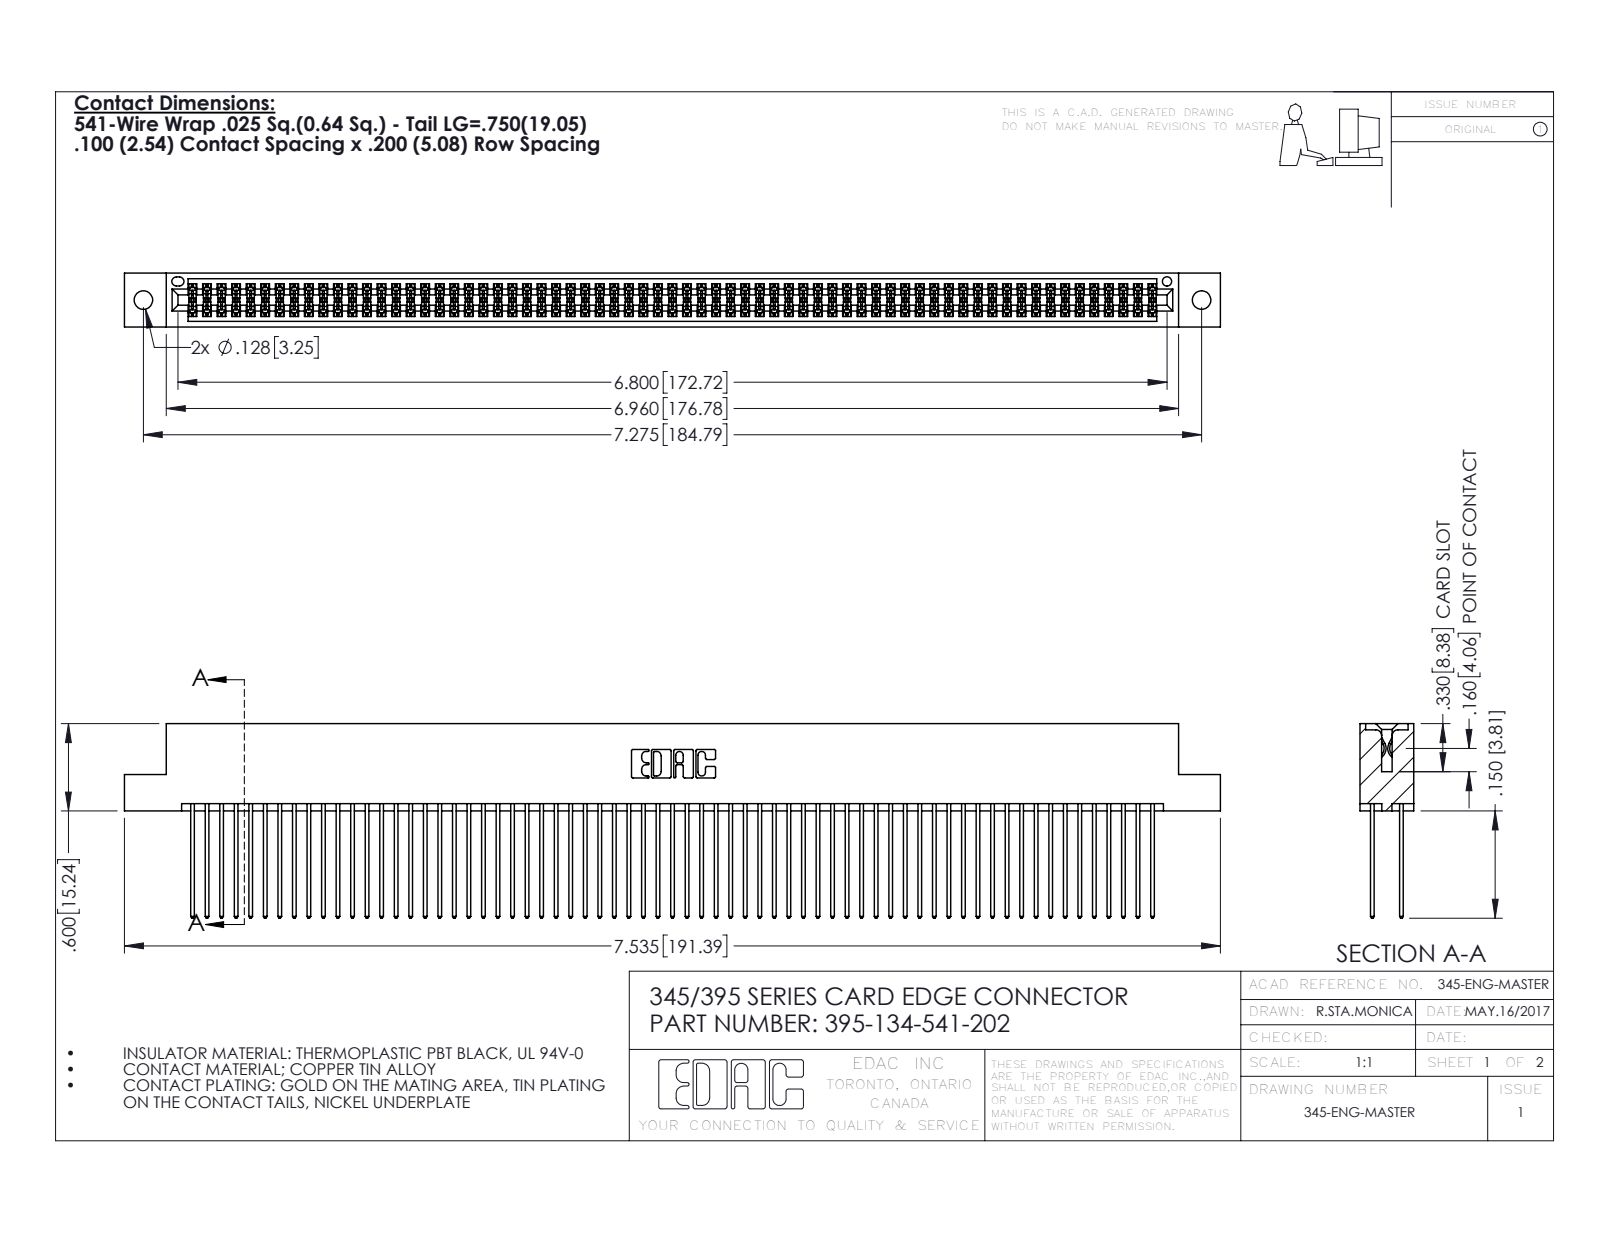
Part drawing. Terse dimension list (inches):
name: 395-134-541-202; 345-292-001_345-293-141; 345 Part_Flush Mounting Lugs - 0.128 Dia
written by: SolidWorks 2016 (CONFIG_CONTROL_DESIGN)
unit: in
bodies: 135 solids, 6826 faces (4502 planar, 2324 cylindrical, 0 other)
size: 7.535 × 1.337 × 0.37
volume: 1.193 in³; area: 50.74 in²
holes: 2× ⌀0.128, 1× ⌀0.064
rounds: 201× R0.006, 134× R0.01, 22× R0.01, 6× R0.007, 6× R0.031, 3× R0.026, 2× R0.014, 2× R0.019
face distances: 0.298, 0.072, 0.2, 0.098, 0.272, 0.025, 0.225, 0.37, 0.175, 0.149
hole spacings: 0.27, 7.039, 7.275
